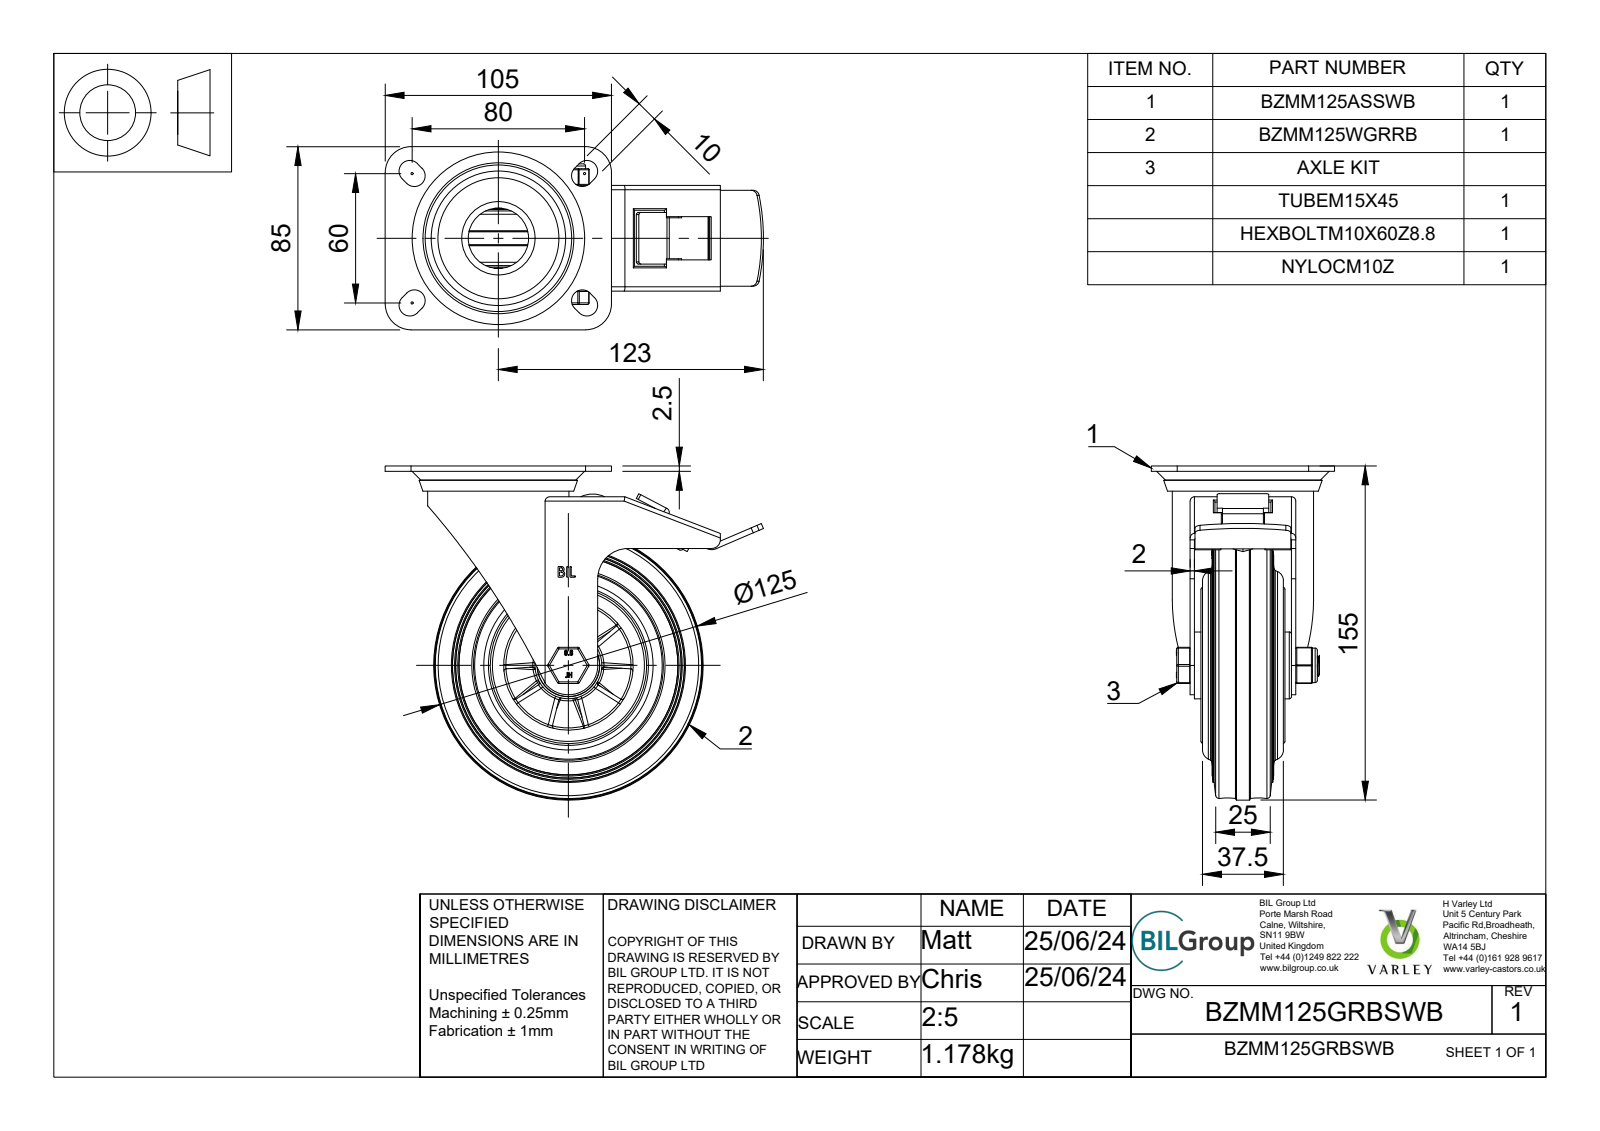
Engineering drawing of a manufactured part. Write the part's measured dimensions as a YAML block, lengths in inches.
part_name: "BZMM125GRBSWB v3; BZMM125ASSWB v1; ZINC PLATED, PRESSED STEEL TOP PLATE; ZINC PLATED, PRESSED STEEL FORKS (+8 more)"
step_written_by: "Autodesk Translation Framework v13.14.0.145 (AUTOMOTIVE_DESIGN)"
units: inches
bodies: {solids: 24, faces: 1040, planar: 409, cylindrical: 238, other: 393}
overall_size: [6.909, 6.102, 3.346]
volume: 25.26
surface_area: 261.8
round_holes:
  - {diameter: 0.236, count: 2}
  - {diameter: 0.394, count: 1}
  - {diameter: 0.402, count: 1}
  - {diameter: 0.472, count: 1}
  - {diameter: 0.591, count: 1}
  - {diameter: 0.598, count: 1}
  - {diameter: 0.896, count: 1}
  - {diameter: 1.102, count: 1}
  - {diameter: 1.142, count: 1}
  - {diameter: 1.575, count: 1}
  - {diameter: 2.362, count: 1}
  - {diameter: 2.421, count: 1}
round_bosses_or_shafts:
  - {diameter: 0.157, count: 8}
  - {diameter: 4.921, count: 1}
  - {diameter: 2.579, count: 1}
  - {diameter: 1.339, count: 1}
  - {diameter: 1.22, count: 1}
  - {diameter: 1.138, count: 1}
  - {diameter: 0.63, count: 1}
  - {diameter: 0.61, count: 1}
partial_cylinders:
  - {radius: 0.02, count: 18}
  - {radius: 0.03, count: 16}
  - {radius: 0.059, count: 12}
  - {radius: 0.197, count: 9}
  - {radius: 0.039, count: 8}
  - {radius: 0.079, count: 6}
  - {radius: 0.118, count: 4}
  - {radius: 0.472, count: 4}
face_to_face_distances: [0.079, 0.197, 1.85, 0.098, 0.374, 0.295, 0.453, 0.276, 0.118, 0.02]
hole_center_spacings: [1.722]
